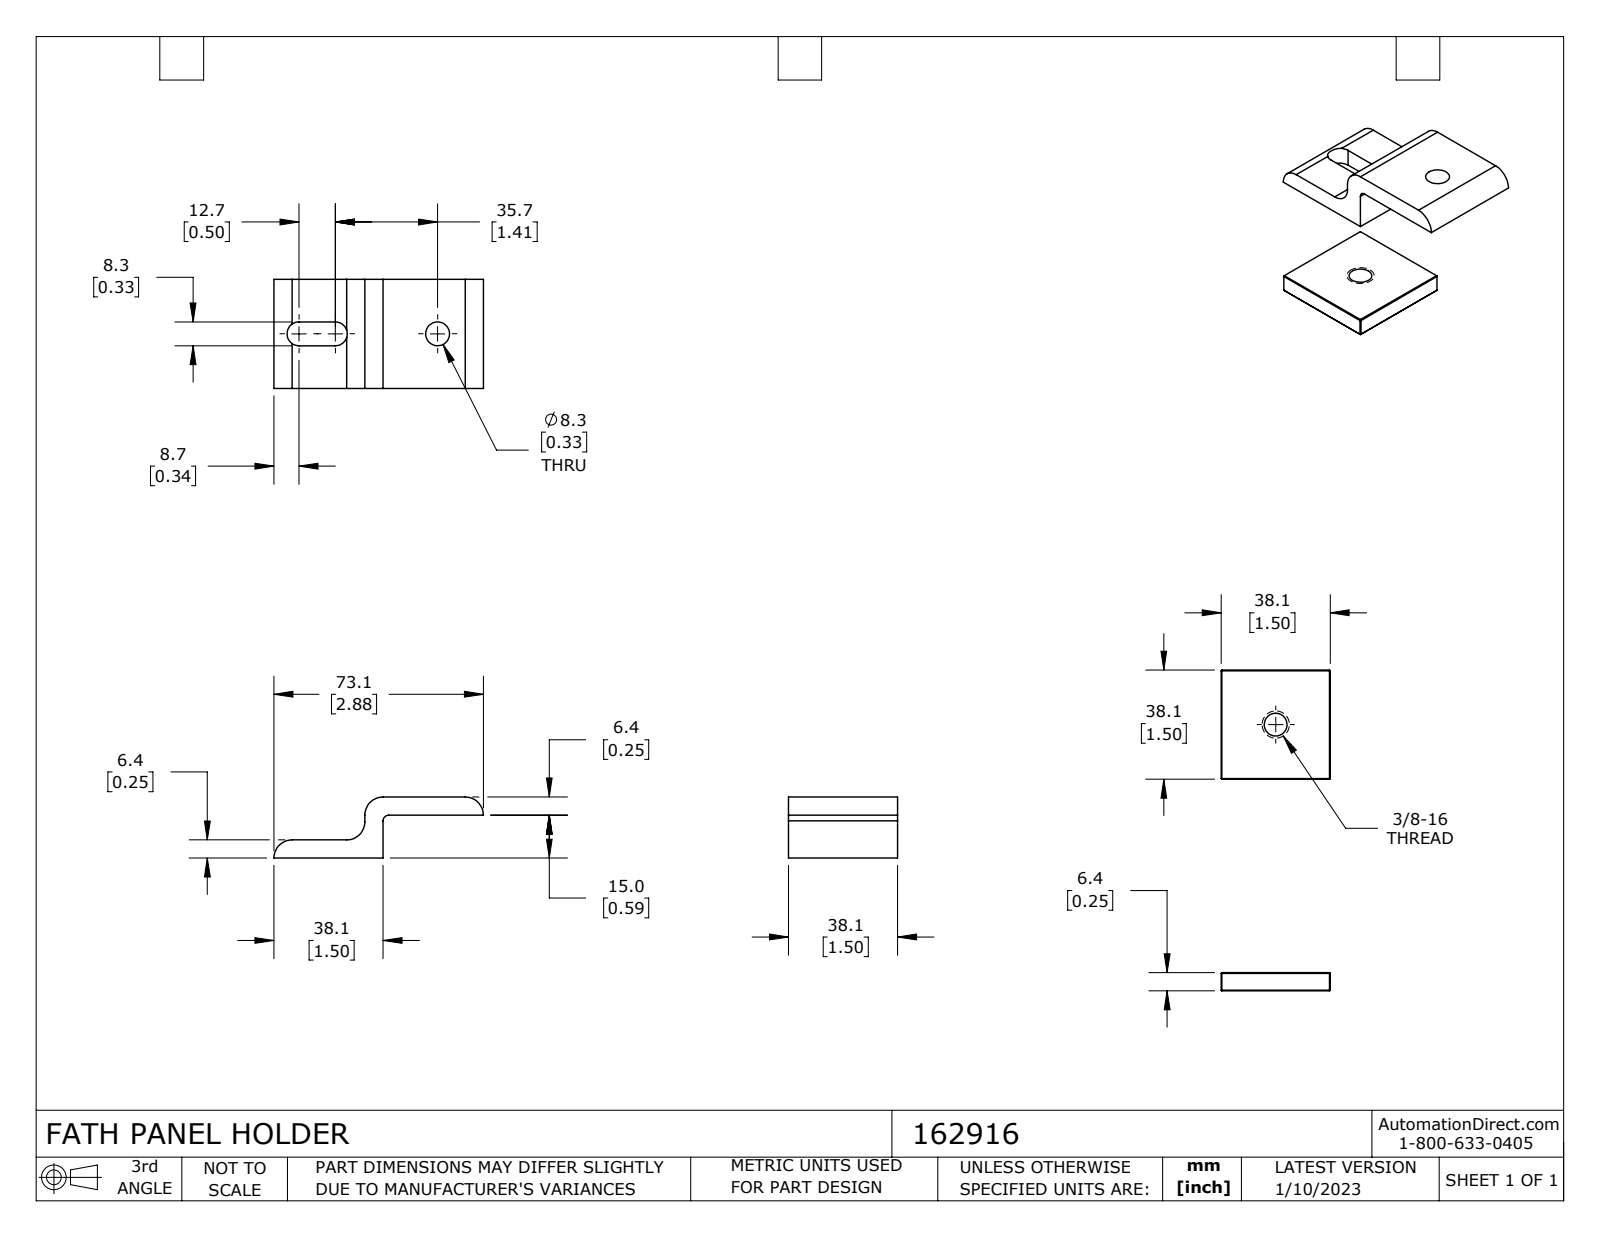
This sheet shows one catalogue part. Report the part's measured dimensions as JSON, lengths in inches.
{"part_name": "162916", "step_written_by": "SolidWorks 2021 (CONFIG_CONTROL_DESIGN)", "units": "inches", "bodies": {"solids": 2, "faces": 49, "planar": 37, "cylindrical": 12, "other": 0}, "overall_size": [2.879, 2.665, 1.5], "volume_in3": 1.722, "surface_area_in2": 18.26, "round_holes": [[0.313, 1], [0.328, 1]], "partial_cylinders_radius": [[0.25, 4], [0.164, 2], [0.079, 1]], "face_to_face_distances": [0.25, 2.415, 1.825, 0.59, 1.575, 2.165, 0.84, 2.665, 1.5, 0.34], "hole_center_spacings": [1.5]}
